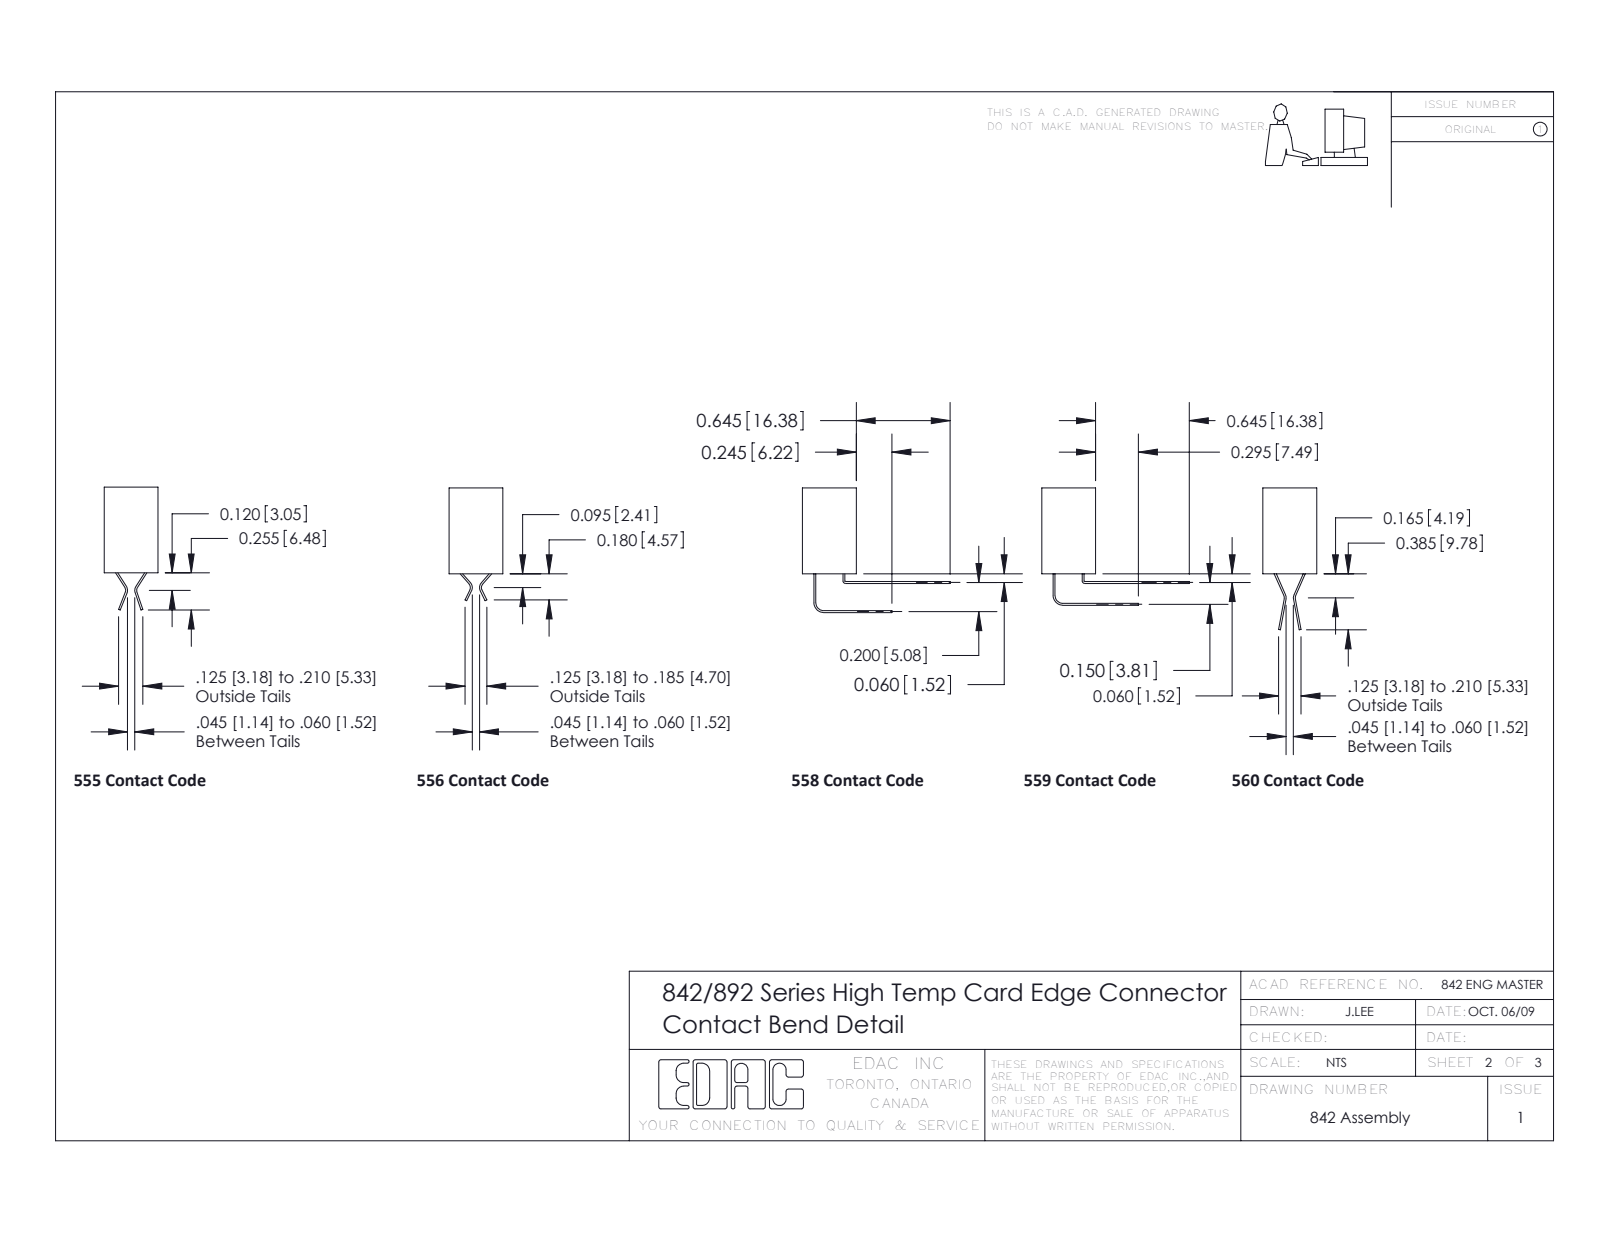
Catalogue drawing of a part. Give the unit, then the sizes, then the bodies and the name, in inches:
Units: inches
Overall size (bounding box): 1.8 × 1.015 × 0.813
Round holes (diameter × count): ⌀0.116 ×2, ⌀0.156 ×2
Round bosses / shafts (diameter × count): ⌀0.25 ×2, ⌀0.18 ×2, ⌀0.136 ×2
Partial cylindrical surfaces — rounded edges, fillets, slot ends (radius × count): R0.006 ×30, R0.01 ×22, R0.007 ×6, R0.031 ×6, R0.026 ×3, R0.014 ×2, R0.022 ×2, R0.024 ×2
Main face-to-face distances: 0.2, 0.072, 0.298, 0.1, 0.3, 0.37, 0.04, 0.025, 0.06, 0.4
Hole centre spacings: 1.522
Volume: 0.25 in³ · Surface area: 10.25 in²
Bodies: 23 solids, 1228 faces (836 planar, 384 cylindrical, 8 other)
Part name (STEP PRODUCT): 342-020-559-203; 342 Part_.156 TH; 342-250-002_345-250-002-102; 345-292-001_559 Tail - 2 (+1 more)
STEP written by: SolidWorks 2016 (CONFIG_CONTROL_DESIGN)
